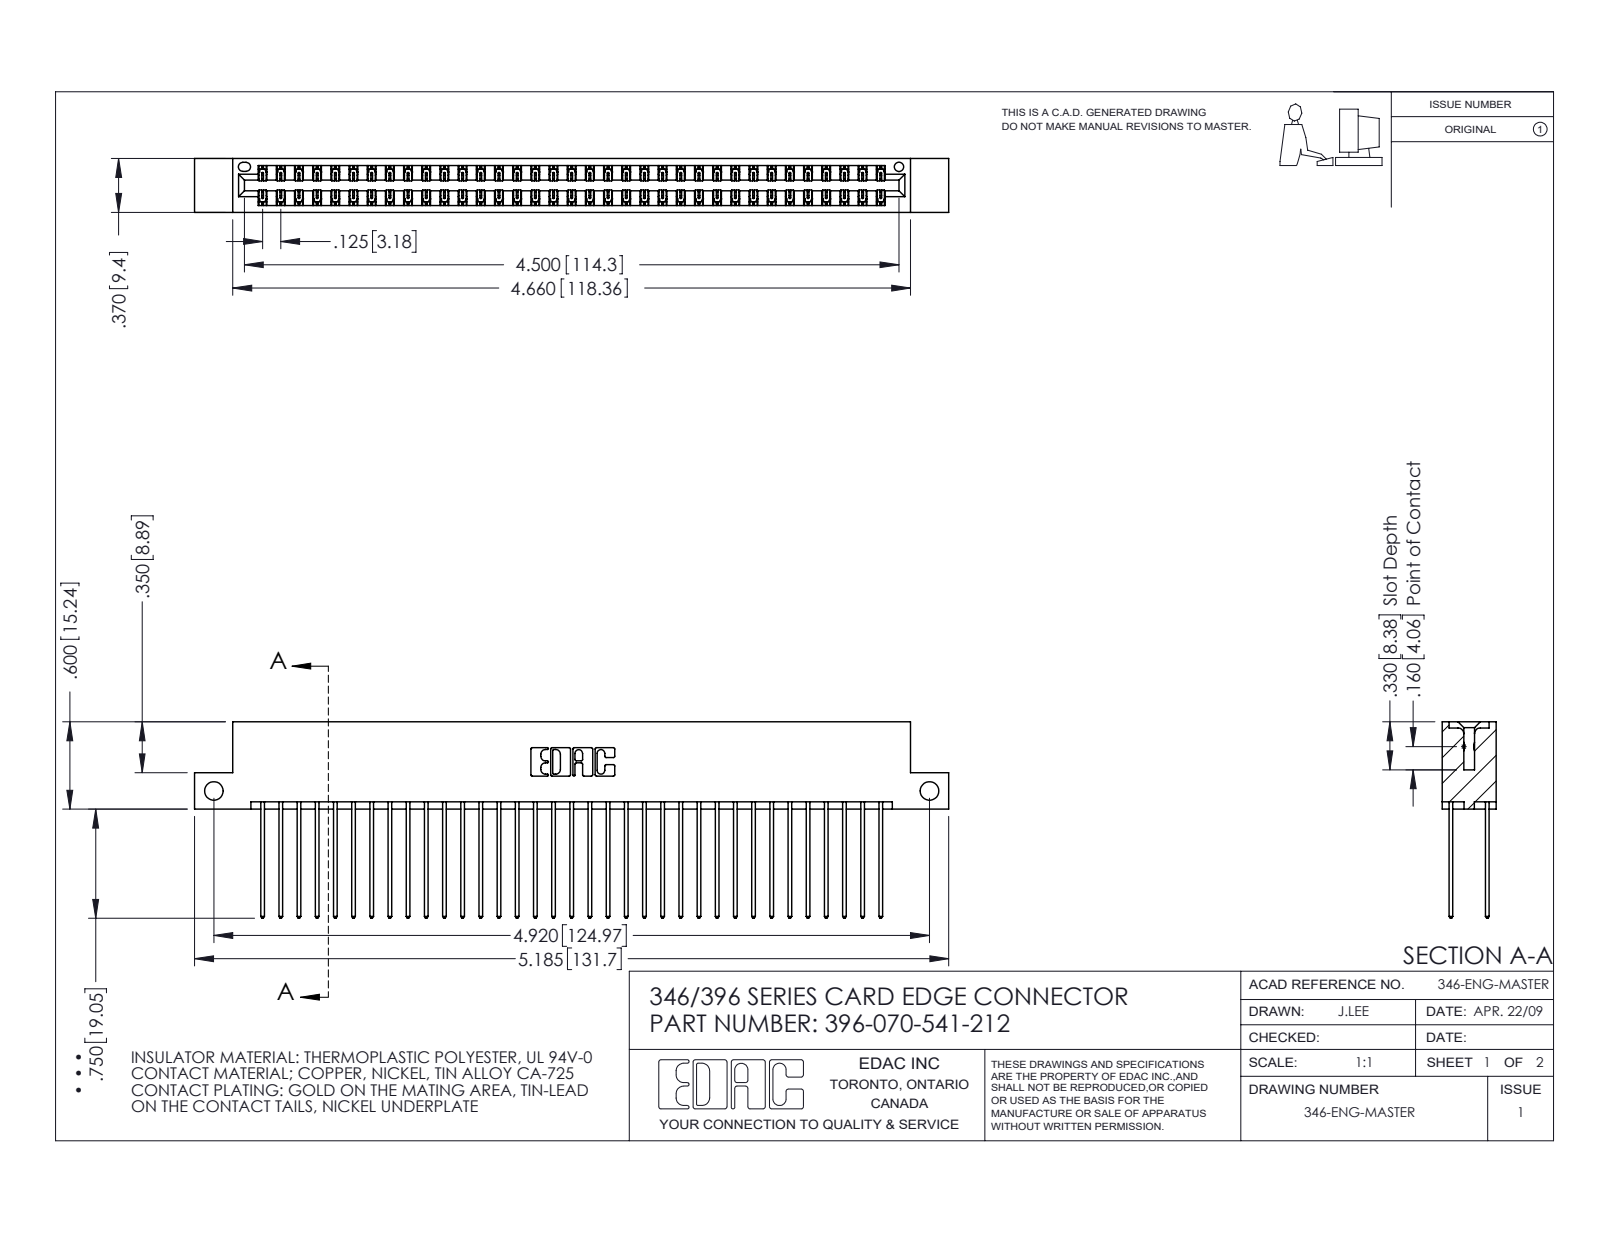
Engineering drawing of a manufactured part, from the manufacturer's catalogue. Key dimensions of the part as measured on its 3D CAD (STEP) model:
Part name (STEP PRODUCT): 396-070-541-212; 346 Part_Flush Mounting Lugs - Side Mount; 345-292-001_345-293-141
STEP written by: SolidWorks 2016 (CONFIG_CONTROL_DESIGN)
Units: inches
Bodies: 71 solids, 3762 faces (2526 planar, 1236 cylindrical, 0 other)
Overall size (bounding box): 5.185 × 1.35 × 0.37
Volume: 0.8 in³ · Surface area: 30.52 in²
Round holes (diameter × count): ⌀0.128 ×2, ⌀0.064 ×1
Partial cylindrical surfaces — rounded edges, fillets, slot ends (radius × count): R0.006 ×105, R0.01 ×70, R0.01 ×22, R0.007 ×6, R0.031 ×6, R0.026 ×3, R0.014 ×2, R0.022 ×2
Main face-to-face distances: 0.048, 0.322, 0.25, 0.072, 0.298, 0.025, 0.37, 0.275, 0.225, 0.148
Hole centre spacings: 4.92
